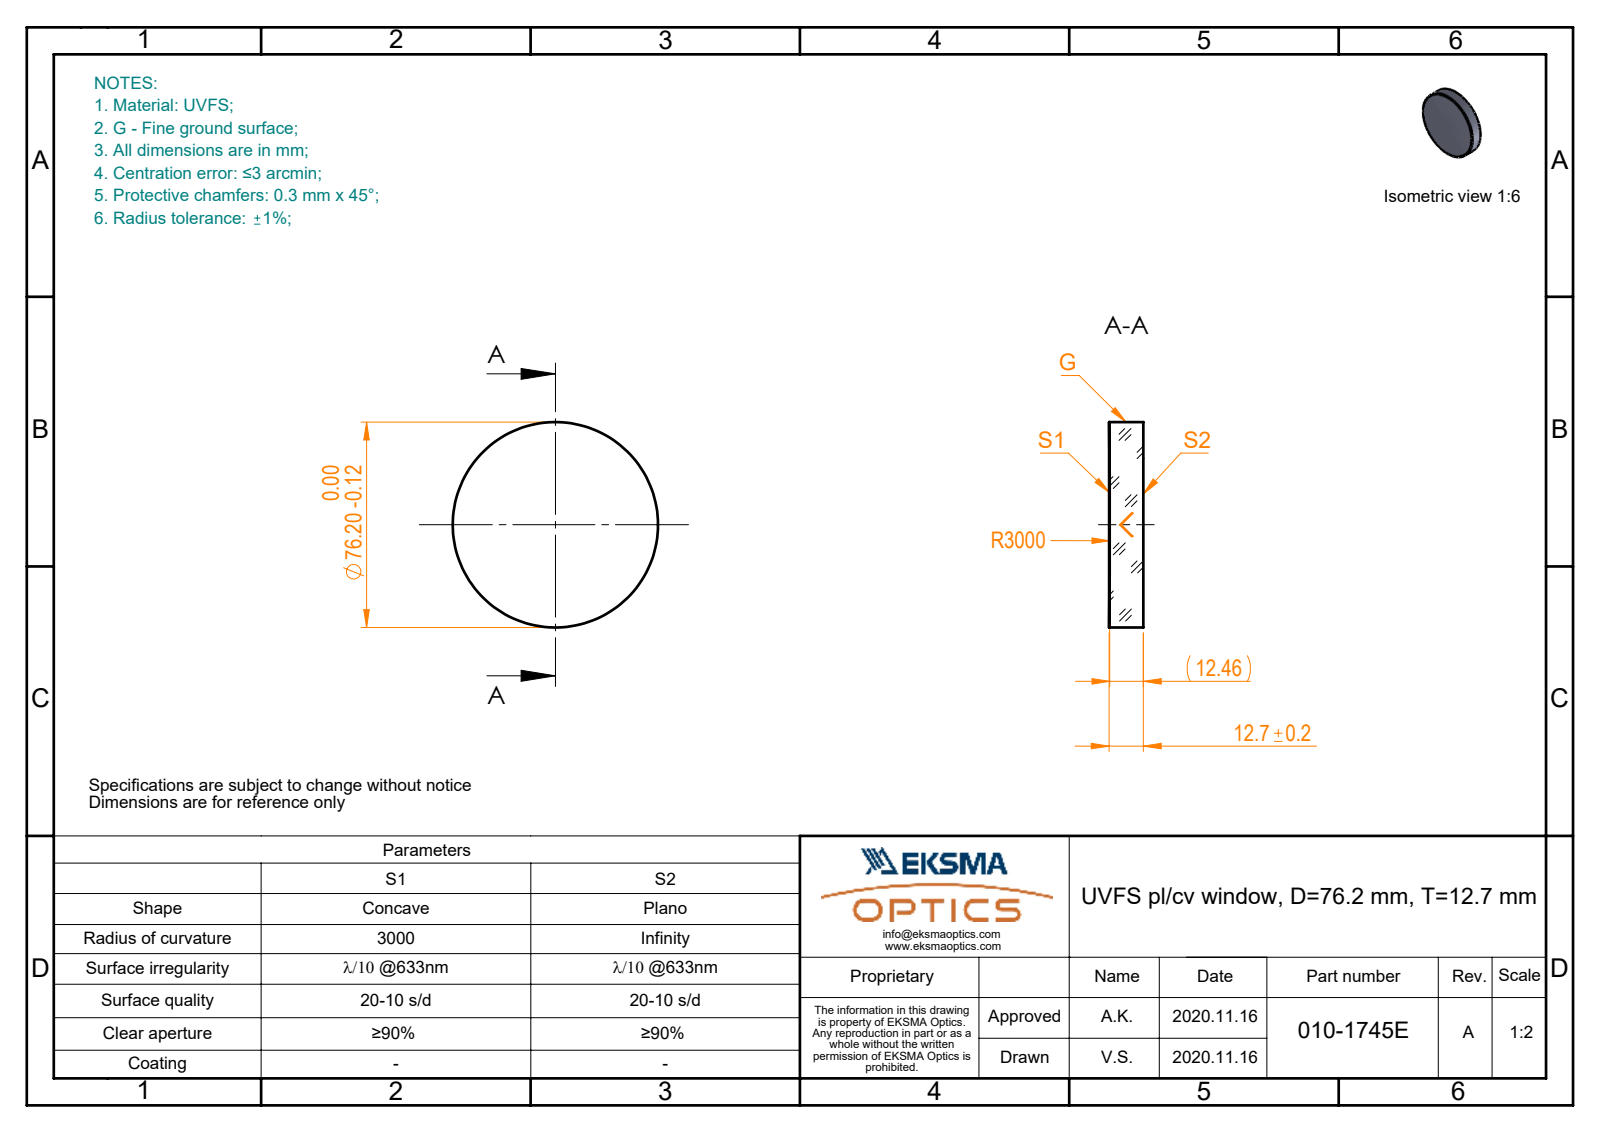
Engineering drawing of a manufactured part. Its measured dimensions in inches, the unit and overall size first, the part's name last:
Units: inches
Overall size (bounding box): 3 × 3 × 0.5
Round bosses / shafts (diameter × count): ⌀3 ×1
Volume: 3.501 in³ · Surface area: 18.85 in²
Bodies: 1 solid, 5 faces (1 planar, 2 cylindrical, 2 other)
Part name (STEP PRODUCT): 010-1745E_UVFS_PCV_window
STEP written by: SolidWorks 2019 (CONFIG_CONTROL_DESIGN)
